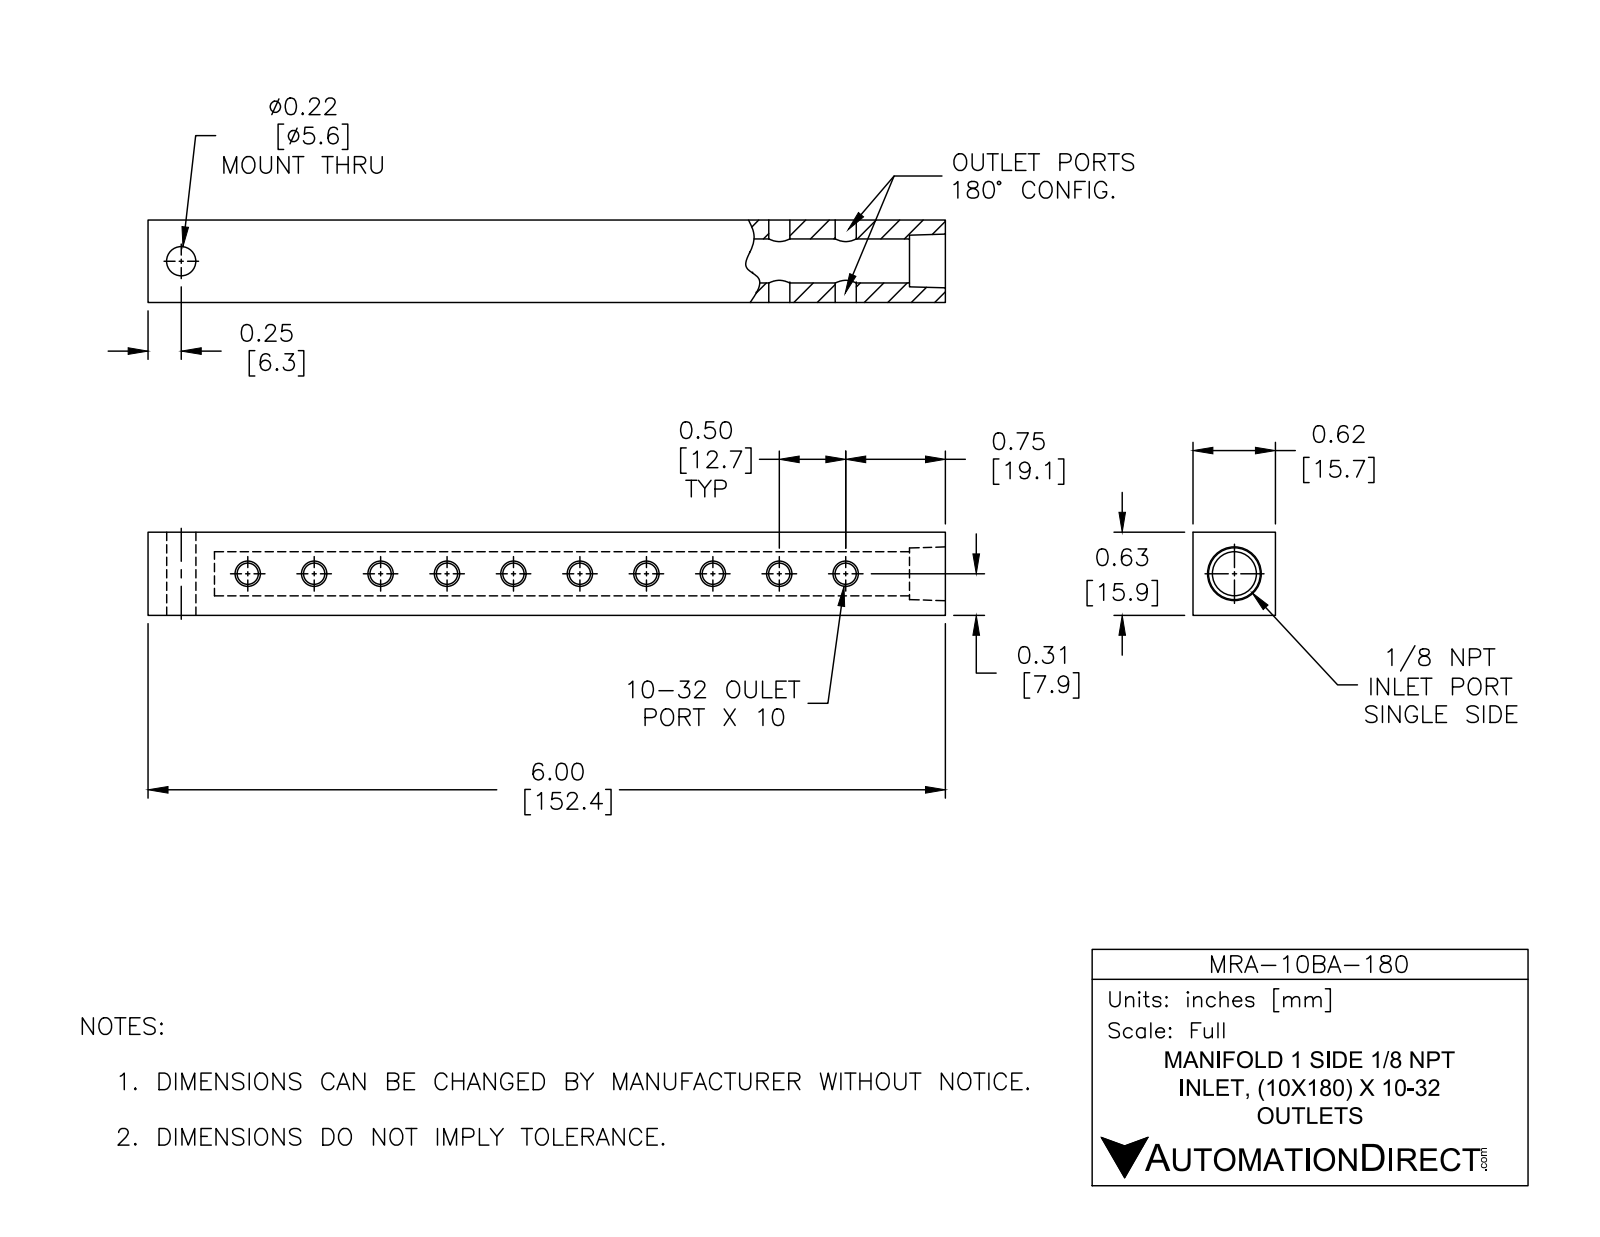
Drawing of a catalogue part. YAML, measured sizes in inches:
part_name: "MRA-10BA-180"
step_written_by: "SolidWorks 2015 (CONFIG_CONTROL_DESIGN)"
units: inches
bodies: {solids: 1, faces: 54, planar: 8, cylindrical: 44, other: 2}
overall_size: [6, 0.625, 0.62]
volume: 1.756
surface_area: 22.58
round_holes:
  - {diameter: 0.159, count: 10}
  - {diameter: 0.22, count: 1}
  - {diameter: 0.332, count: 1}
face_to_face_distances: [0.625, 0.62, 6, 0.5, 5.5, 5.73, 5.23, 0.27]
hole_center_spacings: [0.5, 1, 1.5, 2, 2.5, 3, 3.5, 4]
